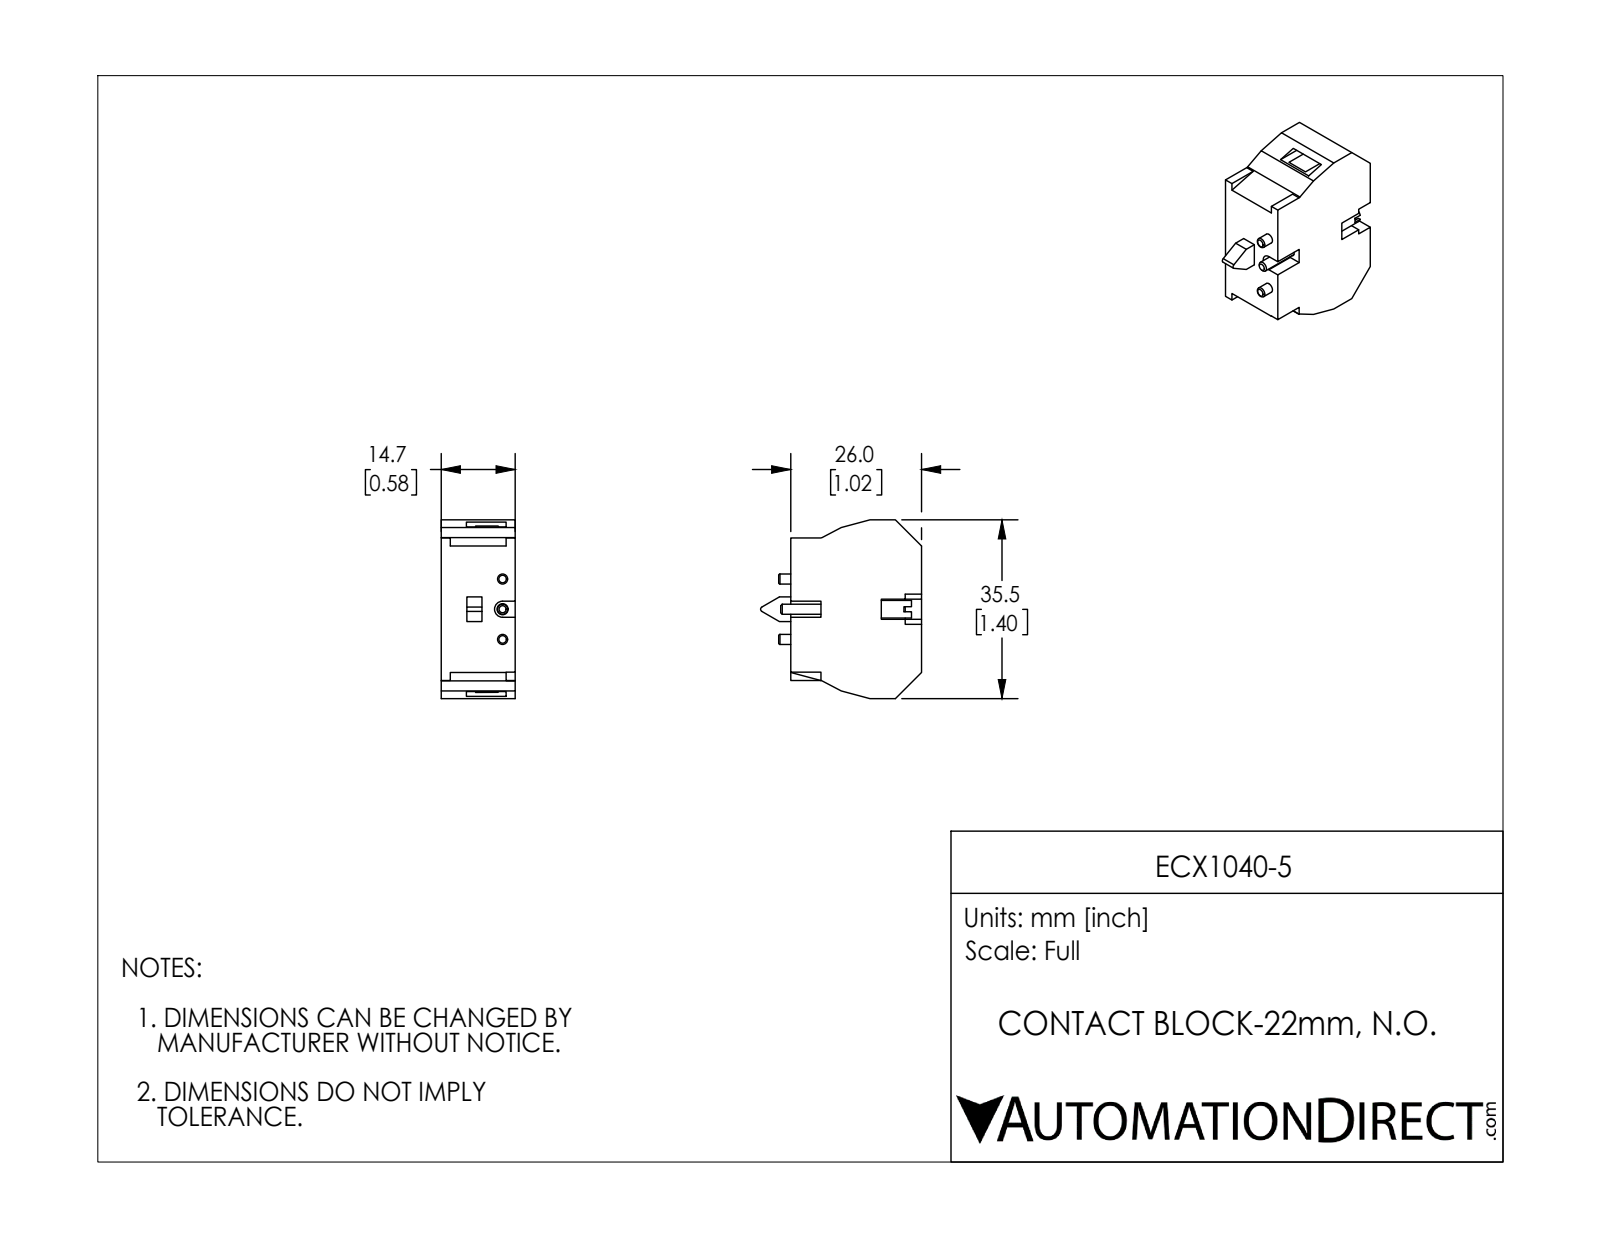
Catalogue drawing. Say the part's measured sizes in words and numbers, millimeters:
The part is named "ECX1040-5". Its 3-D file was written by "SolidWorks 2016 (AUTOMOTIVE_DESIGN)". It is 1 solid with 93 faces: 75 planar, 14 cylindrical and 4 other. Overall it measures 35.54 by 32 by 14.7 millimeters. Its volume is 10 661 cubic millimeters and its surface area 4 346 square millimeters. Round holes: 2 of diameter 2, 1 of diameter 2.2. Partial cylindrical surfaces (rounded edges, fillets, slot ends): 1 of radius 0.5, 1 of radius 1.6, 1 of radius 2. The main face-to-face distances are 14.7, 26, 6.84, 7.86, 0.45, 12.9, 6.87, 28.67, 0.95, 35.09. The hole center spacings are 6, 12.
